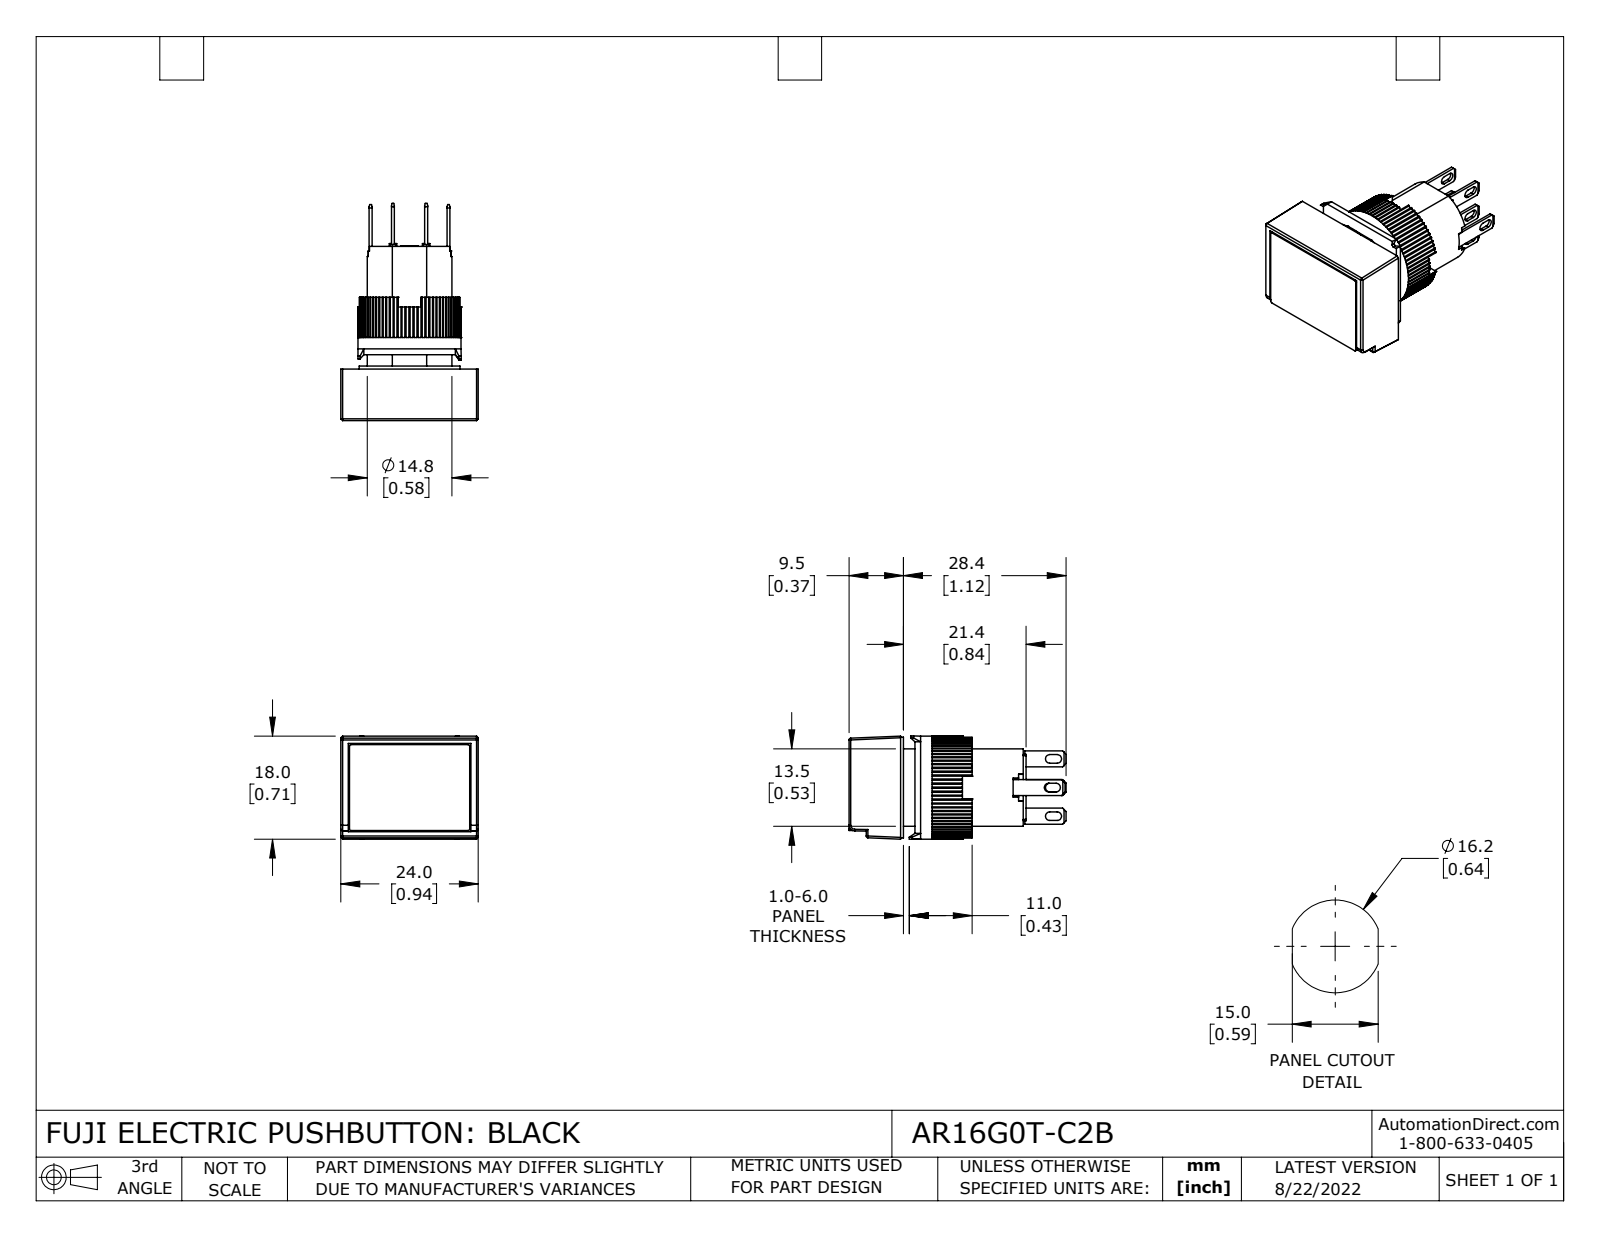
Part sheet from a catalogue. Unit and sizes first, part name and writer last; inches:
Units: inches
Overall size (bounding box): 1.492 × 0.945 × 0.709
Round holes (diameter × count): ⌀0.543 ×1, ⌀0.583 ×1
Round bosses / shafts (diameter × count): ⌀0.709 ×1, ⌀0.693 ×1
Partial cylindrical surfaces — rounded edges, fillets, slot ends (radius × count): R0.01 ×80, R0.008 ×12, R0.03 ×8, R0.012 ×6, R0.039 ×1
Main face-to-face distances: 0.213, 0.354, 0.142, 0.35, 0.492, 0.138, 0.02, 0.843, 0.059, 0.453
Volume: 0.448 in³ · Surface area: 9.503 in²
Bodies: 14 solids, 841 faces (654 planar, 181 cylindrical, 6 other)
Part name (STEP PRODUCT): AR16G0T-C2B
STEP written by: SolidWorks 2021 (CONFIG_CONTROL_DESIGN)
